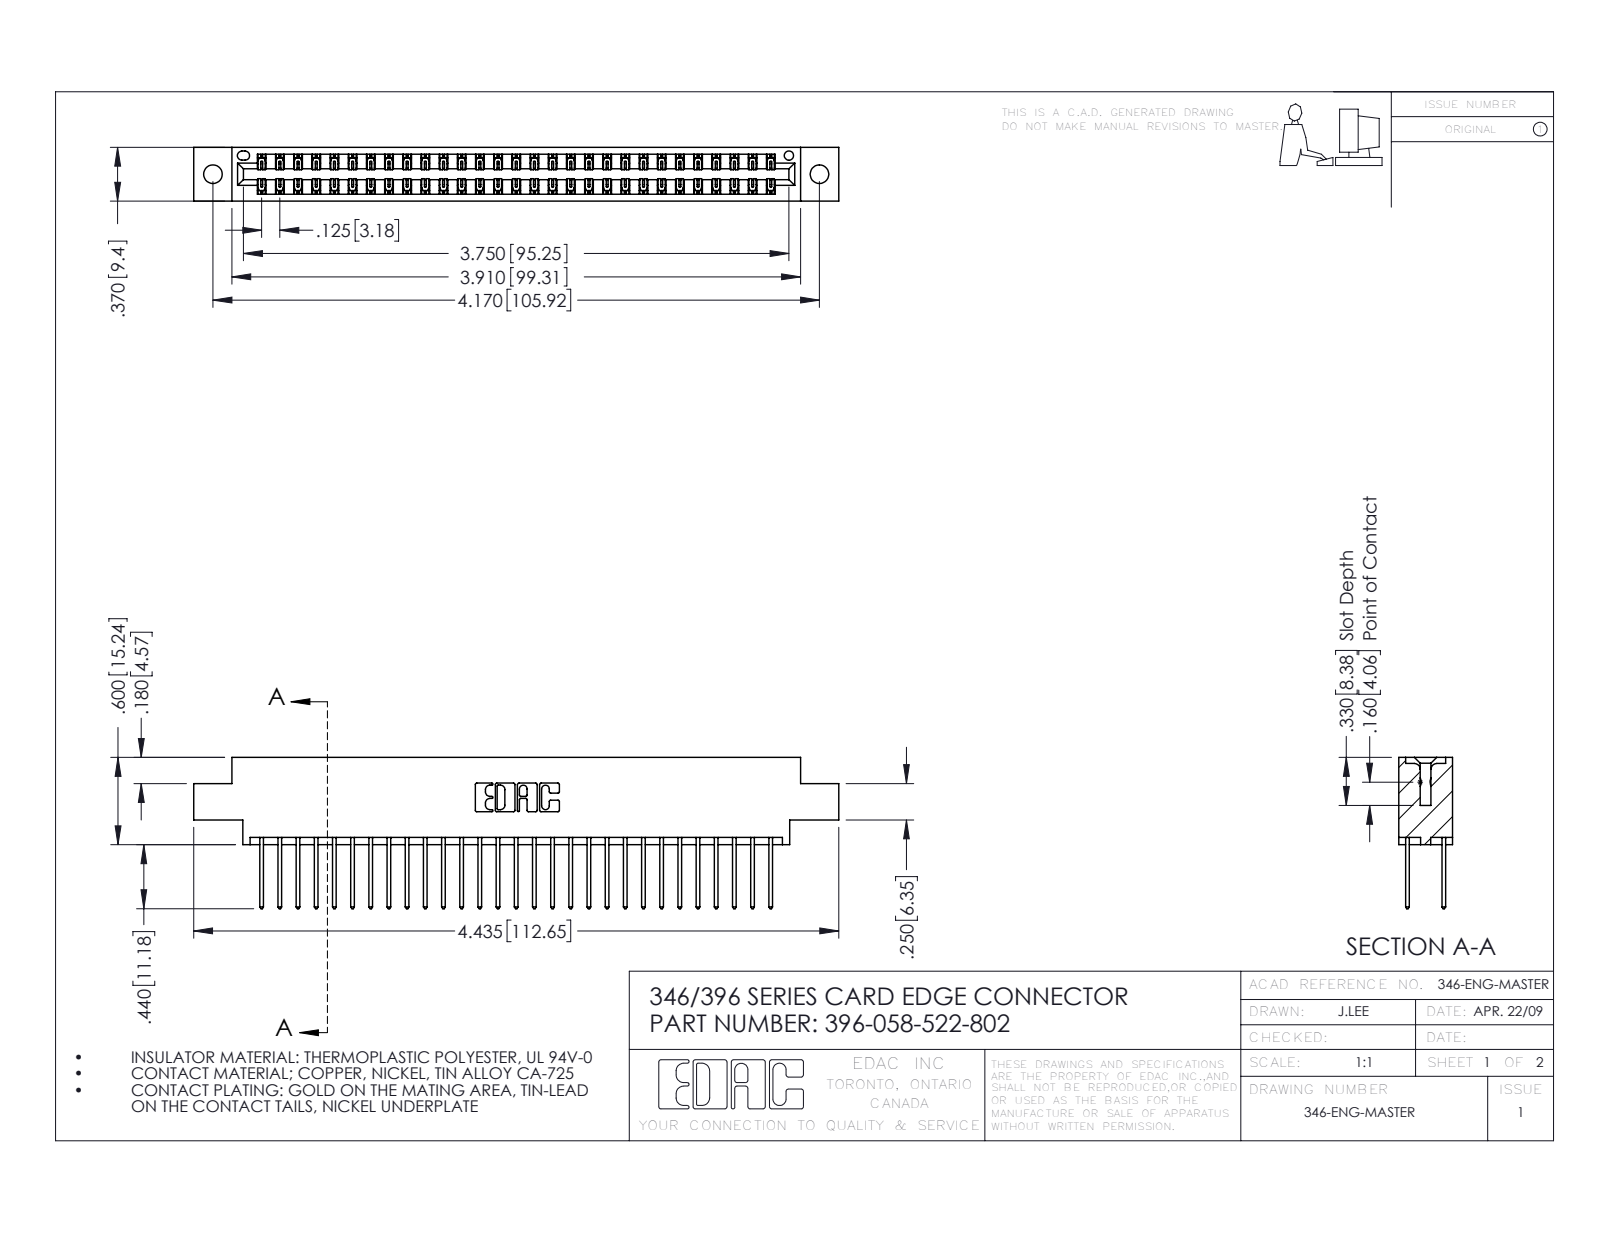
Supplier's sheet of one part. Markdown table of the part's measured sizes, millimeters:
| quantity | value |
| --- | --- |
| part name | 346 Part_0.170 Offset - 0.128 Dia; 345-292-001_345-293-122; 396-058-522-802 |
| STEP written by | SolidWorks 2016 (CONFIG_CONTROL_DESIGN) |
| units | millimeters |
| bodies | 59 solids, 3142 faces (2110 planar, 1032 cylindrical, 0 other) |
| overall size | 112.6 × 26.4 × 9.4 |
| volume | 10 800 mm³ |
| surface area | 15 300 mm² |
| round holes (diameter × count) | 3.3 × 2, 1.6 × 1 |
| partial cylindrical surfaces (radius × count) | 0.2 × 87, 0.3 × 58, 0.3 × 22, 0.2 × 6, 0.8 × 6, 0.7 × 3, 0.4 × 2, 0.6 × 2 |
| main face-to-face distances | 1.2, 8.2, 6.4, 9.4, 1.8, 7.6, 0.6, 7, 3.8, 5.6 |
| hole center spacings | 6.2, 100.6, 105.9 |
